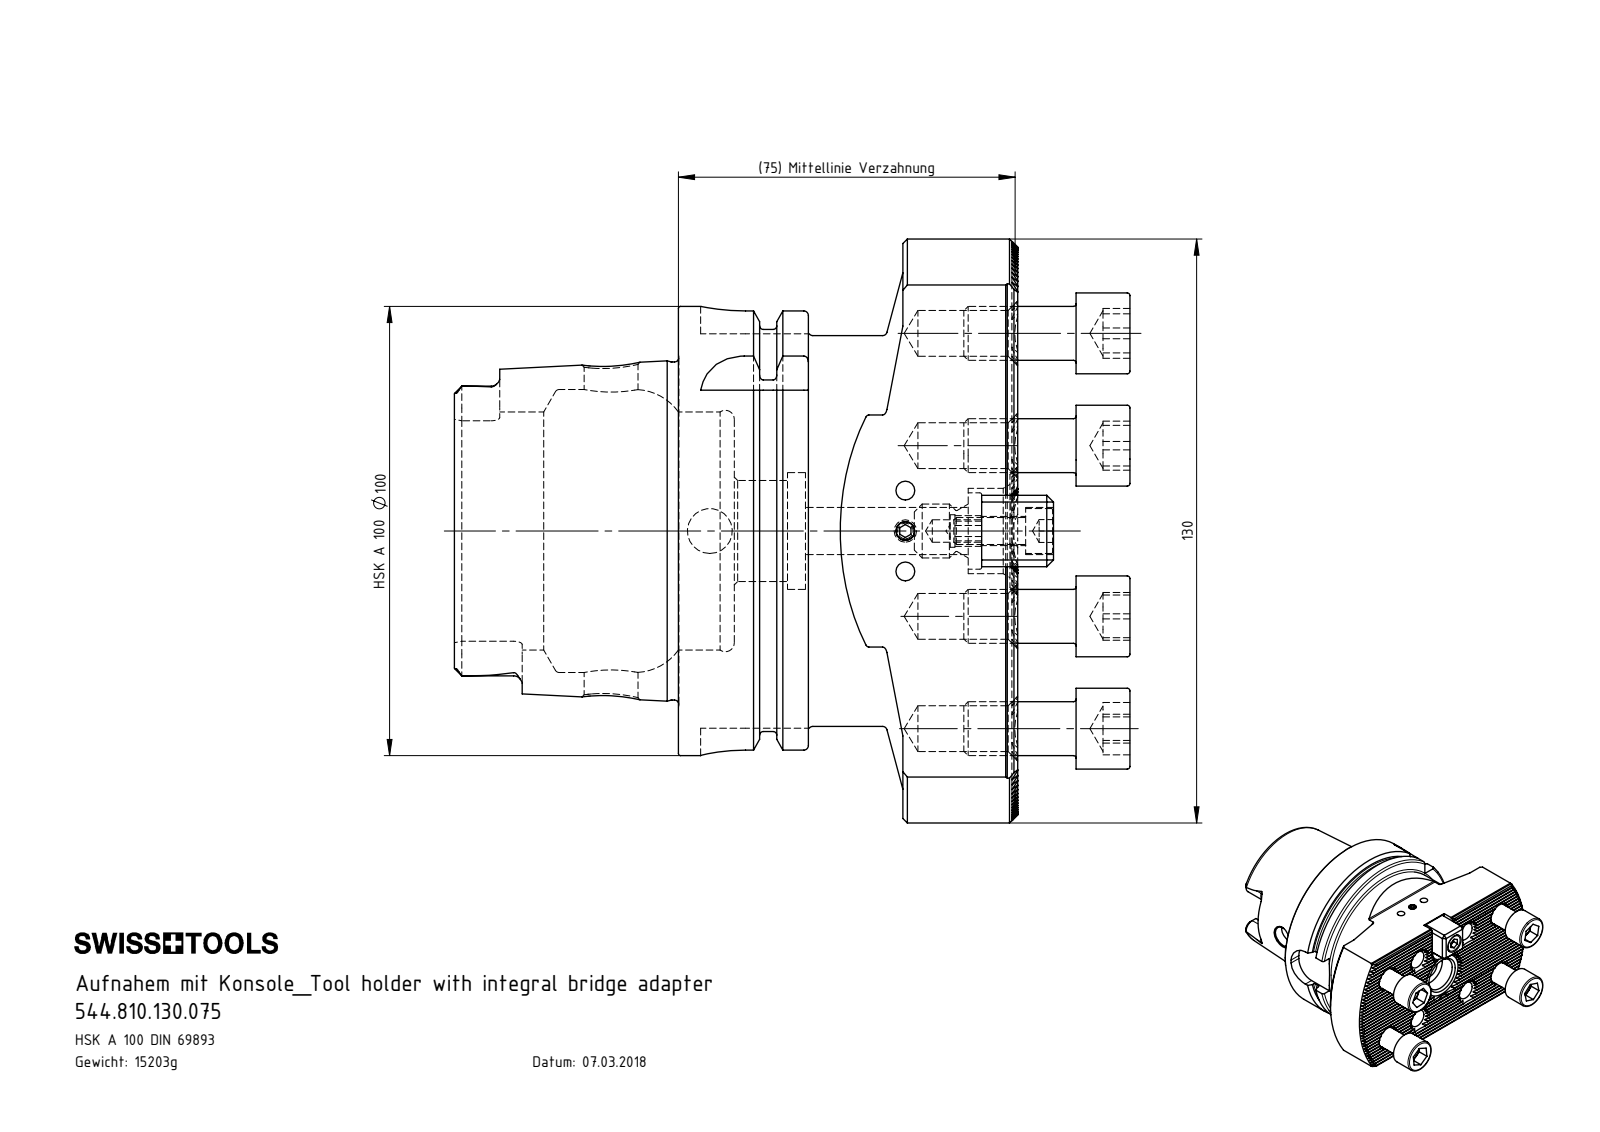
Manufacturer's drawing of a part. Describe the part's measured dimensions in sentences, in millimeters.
The part is named "DIN 908 - M12x1.5; HA0-Ko1.K01.075_A_Fertigbearbeitung; ISO 4762 - M12 x 25; ISO 4762 - M6 x 16 (+3 more)". Its 3-D file was written by "SolidWorks 2015 (AUTOMOTIVE_DESIGN)". It is 10 solids with 928 faces: 513 planar, 223 cylindrical and 192 other. Overall it measures 150.48 by 130 by 100 millimeters. Its volume is 593 015 cubic millimeters and its surface area 96 778 square millimeters. Round holes: 8 of diameter 10.2, 3 of diameter 4.2, 2 of diameter 10.5, 1 of diameter 5, 1 of diameter 6.5, 1 of diameter 7.24, 1 of diameter 10, 1 of diameter 12, 1 of diameter 19, 1 of diameter 22.5, 1 of diameter 26, 1 of diameter 53. Round bosses or shafts: 5 of diameter 12, 4 of diameter 18, 1 of diameter 100, 1 of diameter 91.95, 1 of diameter 87, 1 of diameter 75.26, 1 of diameter 17, 1 of diameter 10. Partial cylindrical surfaces (rounded edges, fillets, slot ends): 34 of radius 0.14, 6 of radius 1.9, 4 of radius 4.88, 4 of radius 10, 2 of radius 0.8, 1 of radius 7.95, 1 of radius 65. The main face-to-face distances are 1.73, 17.32, 70, 8.66, 3.46, 5.2, 6.93, 15.59, 19.05, 3.47. The hole center spacings are 25, 27.59, 40, 47.17, 48.33, 63, 74.63, 9.
